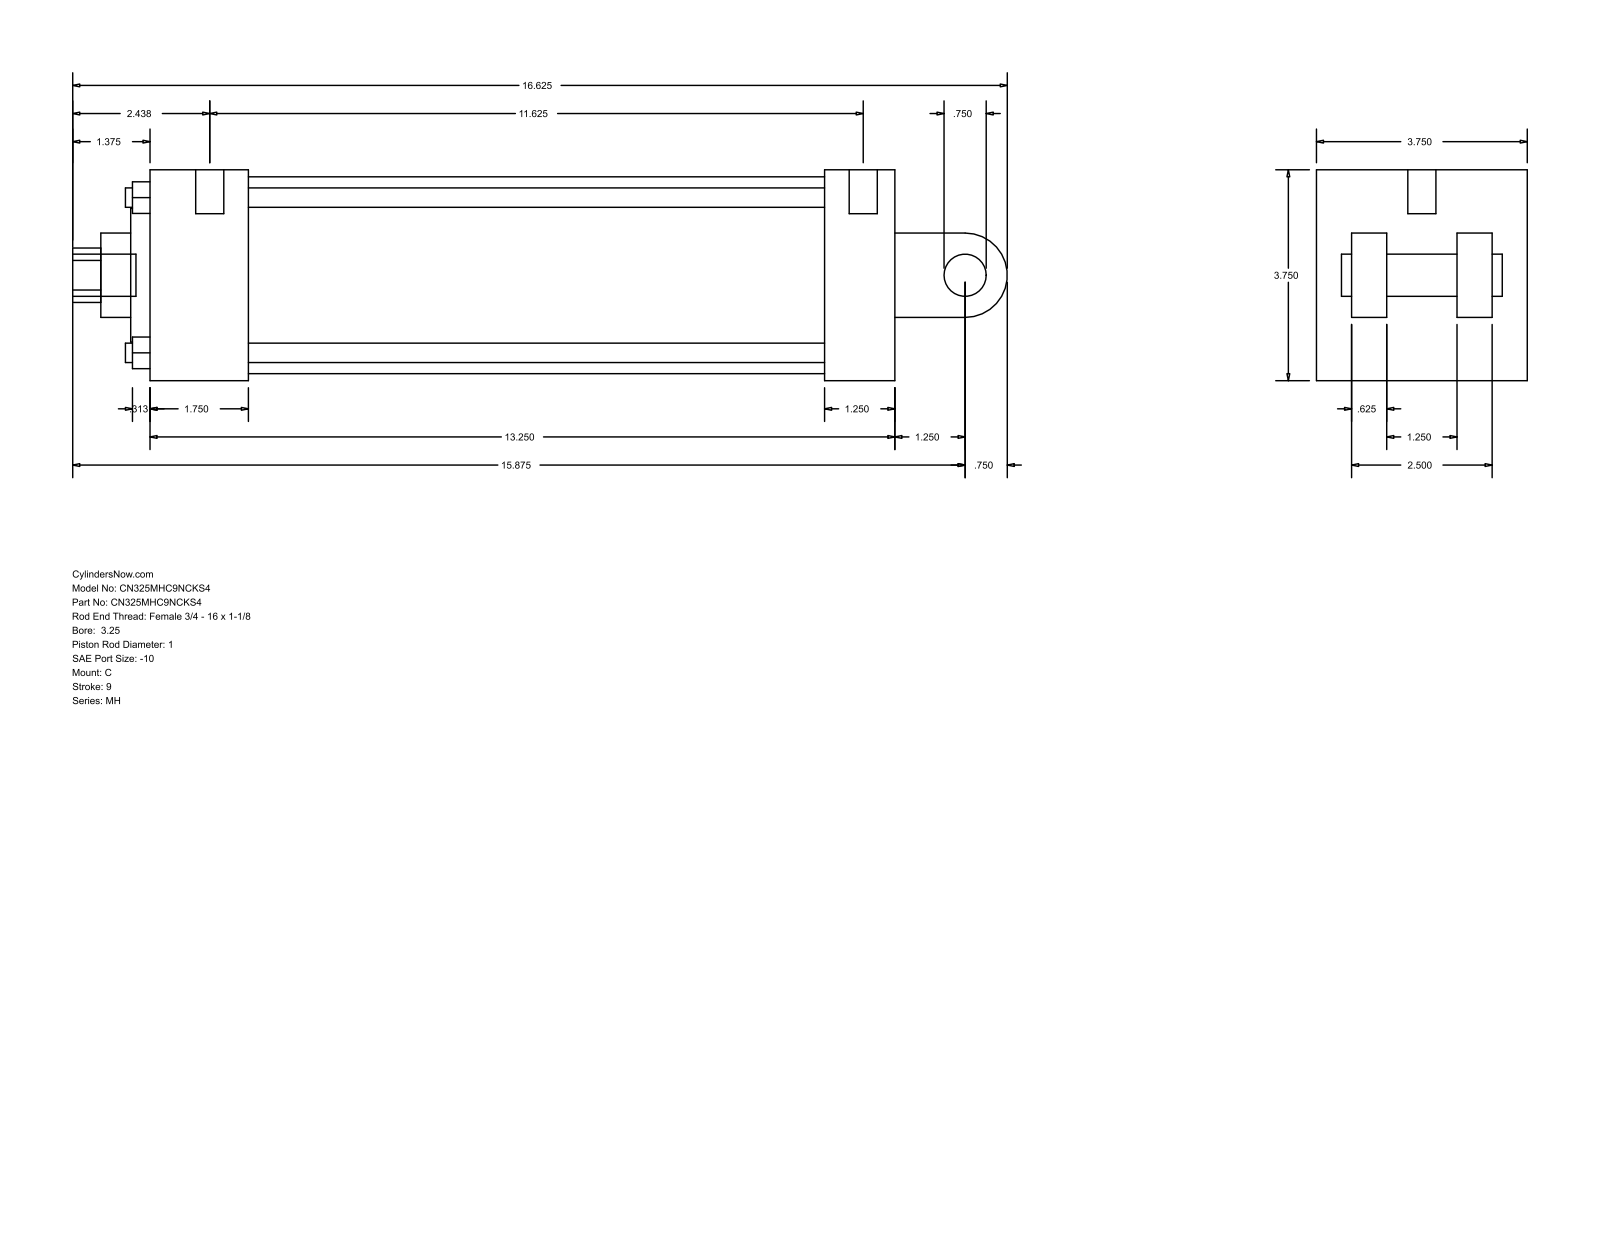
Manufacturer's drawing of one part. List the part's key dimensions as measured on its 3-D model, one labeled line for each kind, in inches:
Part name (STEP PRODUCT): MH_C__0325_1
STEP written by: GSSL Pune (CONFIG_CONTROL_DESIGN)
Units: inches
Bodies: 0 solids, 101 faces (71 planar, 30 cylindrical, 0 other)
Overall size (bounding box): 16.625 × 3.75 × 3.75
Round holes (diameter × count): ⌀0.345 ×4, ⌀0.219 ×2, ⌀0.5 ×1, ⌀1 ×1, ⌀1.5 ×1, ⌀2.375 ×1, ⌀3.5 ×1
Round bosses / shafts (diameter × count): ⌀0.75 ×2, ⌀0.219 ×2, ⌀0.5 ×1
Partial cylindrical surfaces — rounded edges, fillets, slot ends (radius × count): R0.484 ×1, R0.75 ×1
Main face-to-face distances: 3.75, 0.625, 13.25, 2.5, 3.125, 1.25, 1.875, 1.75, 12, 10.25
Hole centre spacings: 1.952, 2.76, 3.903, 0.187
